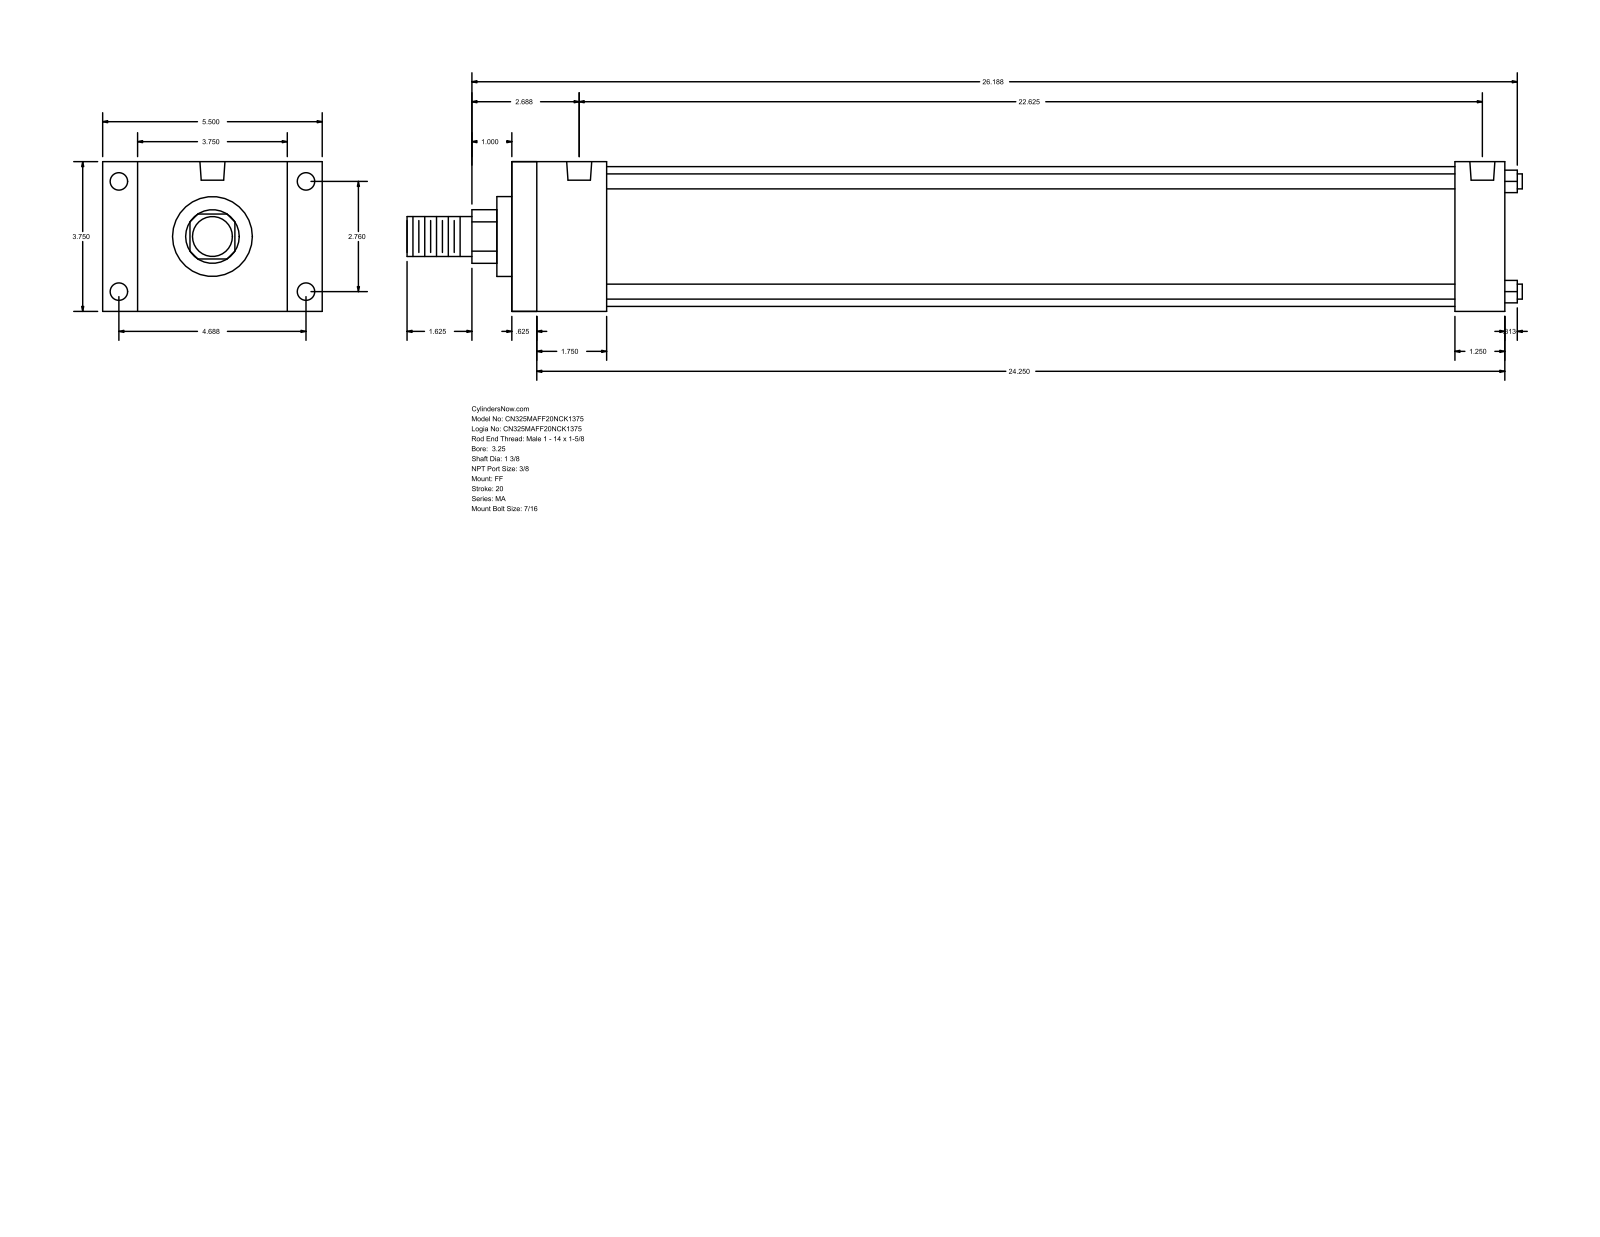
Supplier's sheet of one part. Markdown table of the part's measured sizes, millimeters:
| quantity | value |
| --- | --- |
| part name | MA_FF__0325_1.375 |
| STEP written by | GSSL Pune (CONFIG_CONTROL_DESIGN) |
| units | millimeters |
| bodies | 0 solids, 92 faces (64 planar, 28 cylindrical, 0 other) |
| overall size | 709.61 × 139.7 × 95.25 |
| round holes (diameter × count) | 11.11 × 8, 15.93 × 2 |
| round bosses / shafts (diameter × count) | 9.53 × 4, 88.9 × 1, 50.8 × 1, 34.92 × 1, 25.4 × 1 |
| partial cylindrical surfaces (radius × count) | 17.06 × 1 |
| main face-to-face distances | 95.24, 631.83, 15.87, 615.96, 22.23, 117.47, 60.32, 600.08, 44.45, 584.21 |
| hole center spacings | 4.77, 70.1, 119.06, 138.16, 565.14, 569.91, 574.68 |
